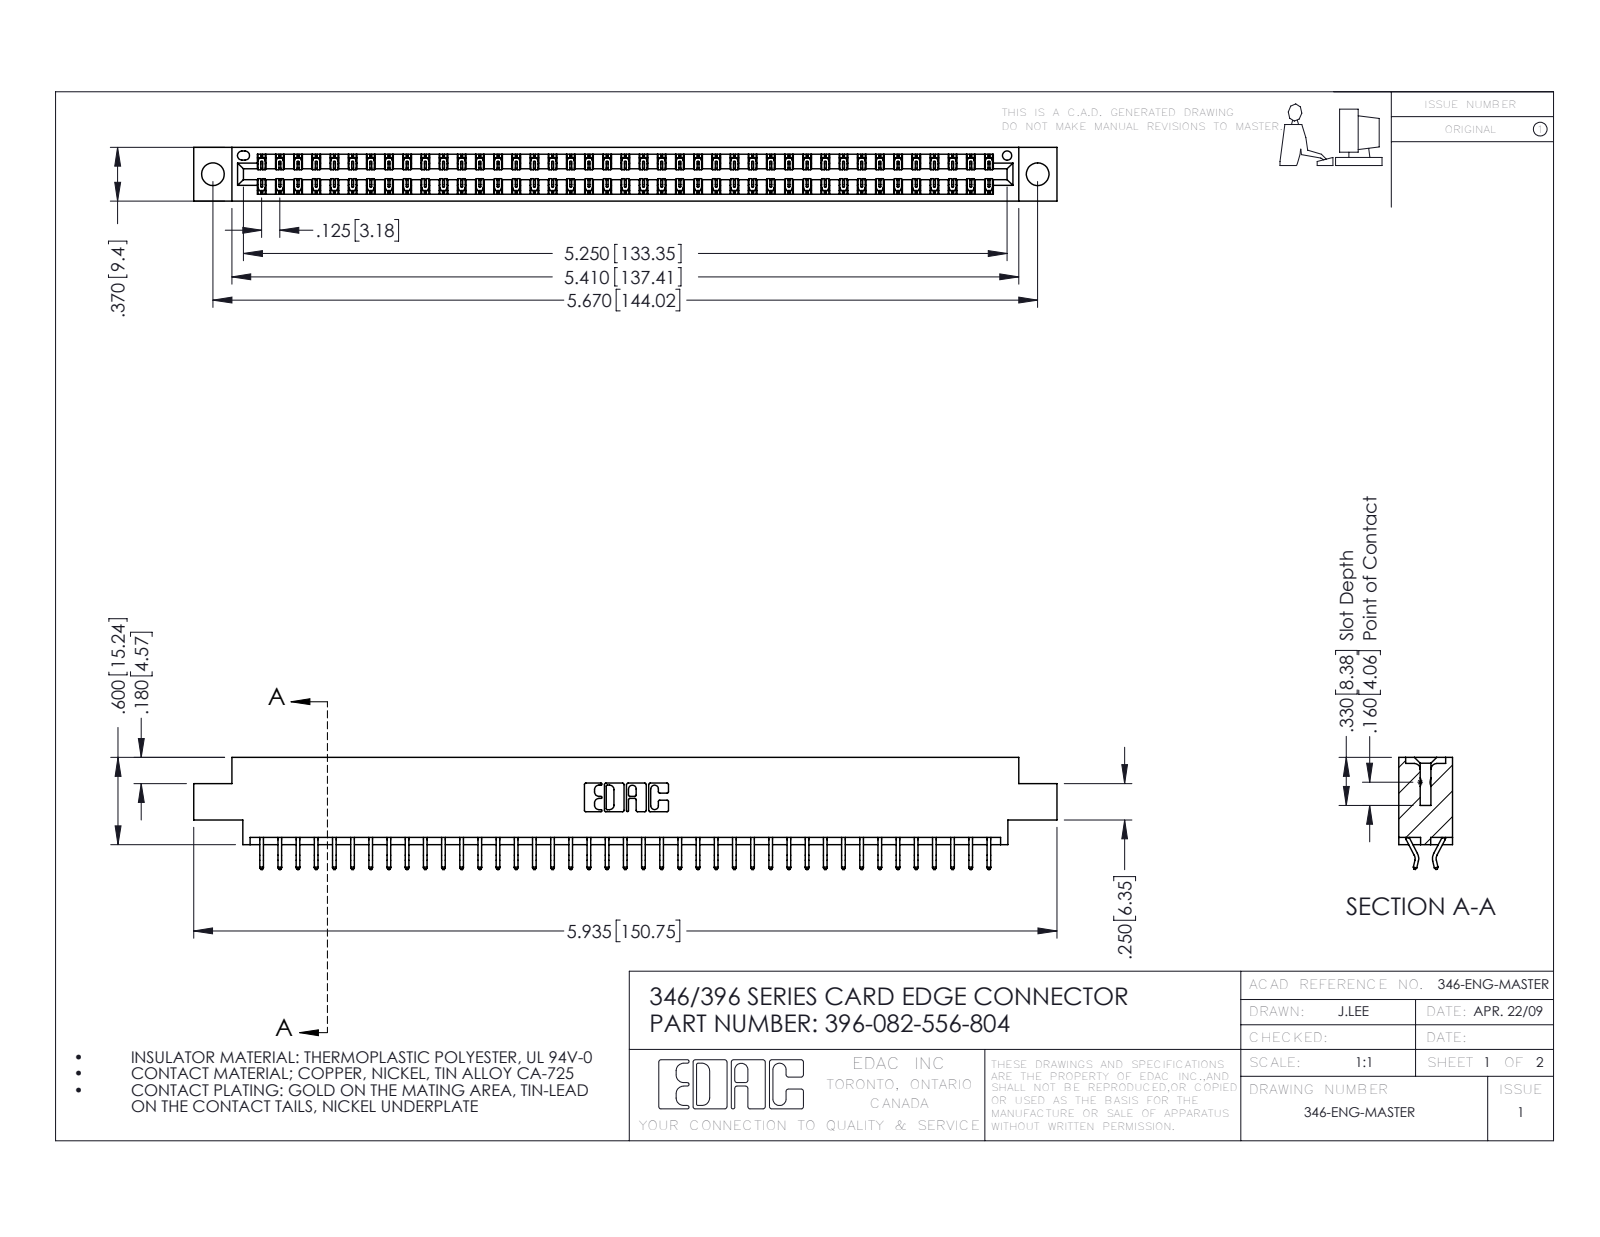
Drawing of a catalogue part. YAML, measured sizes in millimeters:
part_name: "345-292-001_556 Tail; 396-082-556-804; 346 Part_0.170 Offset - 0.156 Dia-TH"
step_written_by: "SolidWorks 2016 (CONFIG_CONTROL_DESIGN)"
units: millimeters
bodies: {solids: 83, faces: 4882, planar: 3278, cylindrical: 1604, other: 0}
overall_size: [150.7, 19.6, 9.4]
volume: 14500
surface_area: 19760
round_holes:
  - {diameter: 4, count: 2}
  - {diameter: 1.6, count: 1}
partial_cylinders:
  - {radius: 0.2, count: 123}
  - {radius: 0.3, count: 22}
  - {radius: 0.2, count: 6}
  - {radius: 0.8, count: 6}
  - {radius: 0.7, count: 3}
  - {radius: 0.3, count: 2}
  - {radius: 0.4, count: 2}
  - {radius: 0.6, count: 2}
face_to_face_distances: [1.2, 8.2, 9.4, 6.4, 0.6, 1.8, 7.6, 7, 3.8, 5.6]
hole_center_spacings: [6.2, 138.7, 144]
